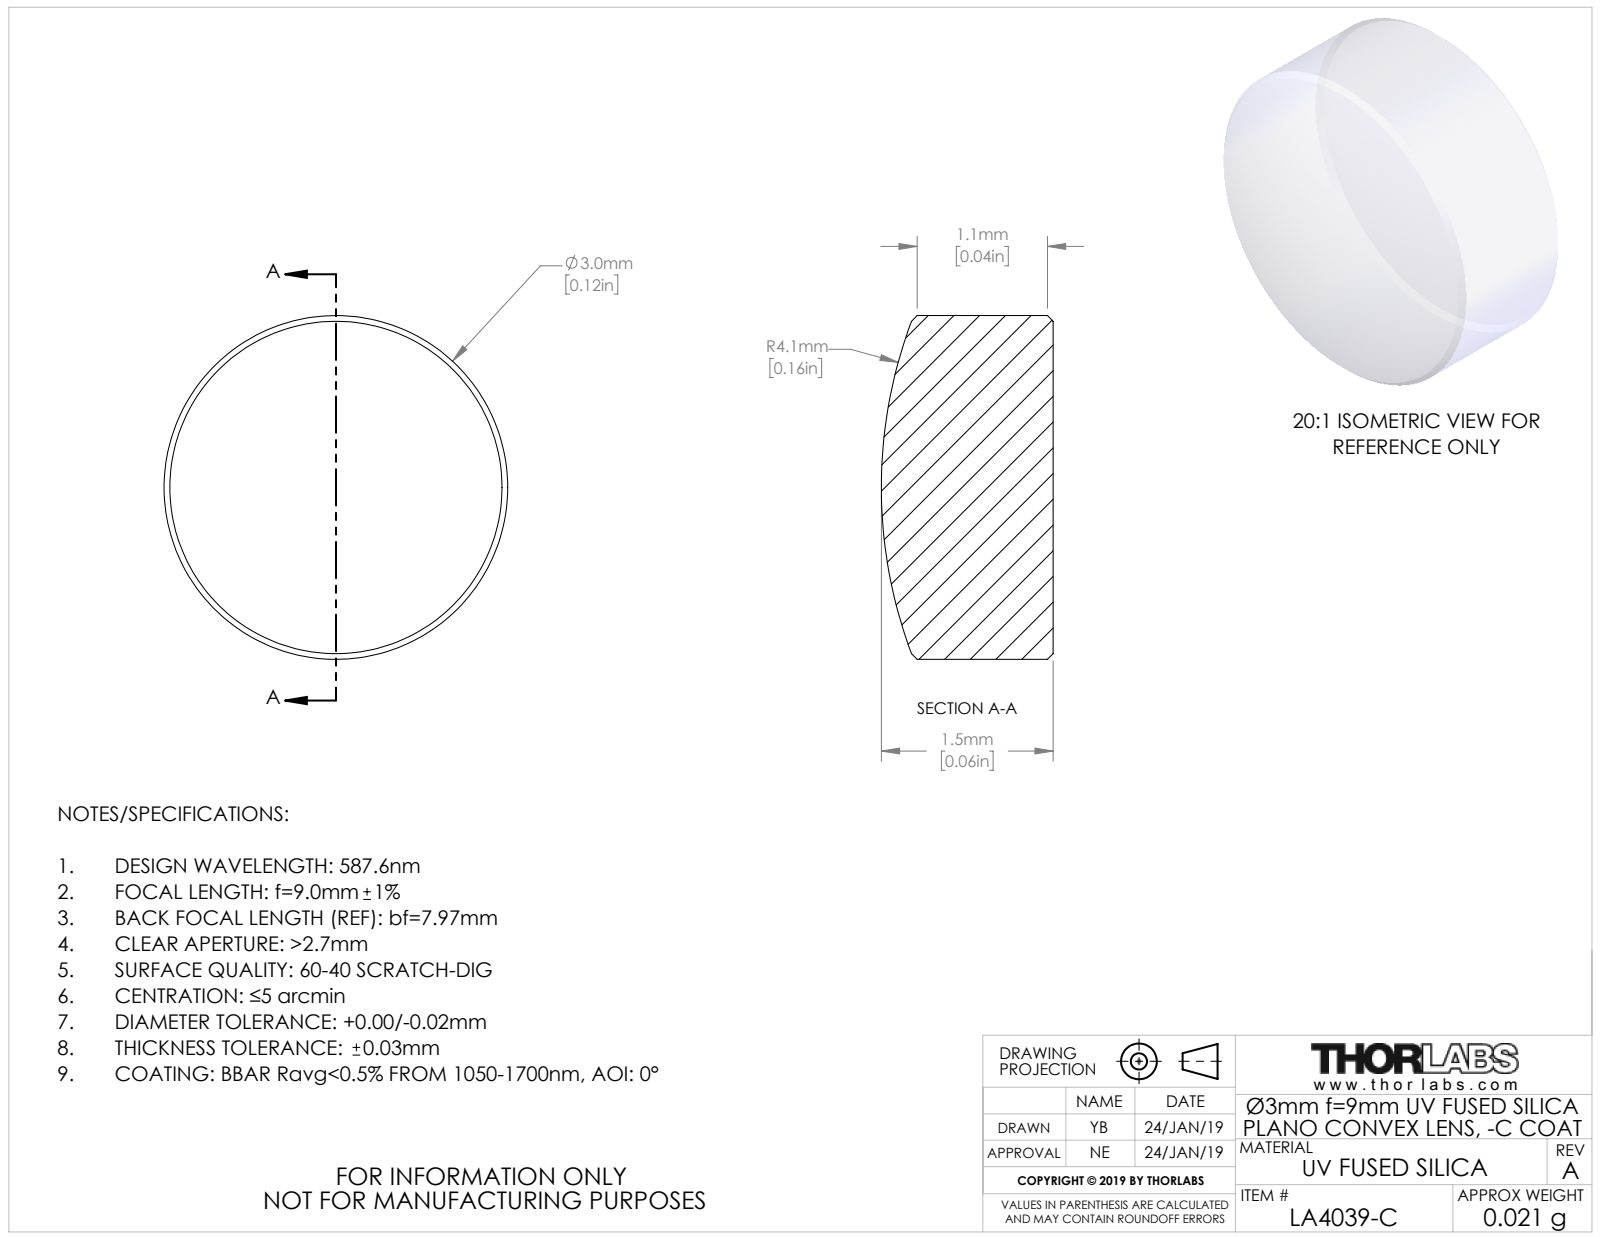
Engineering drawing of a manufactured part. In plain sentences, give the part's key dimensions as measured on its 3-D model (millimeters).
The part is named "TTN162823-E0W". Its 3-D file was written by "SolidWorks 2018 (CONFIG_CONTROL_DESIGN)". It is 1 solid with 9 faces: 1 planar, 2 cylindrical and 6 other. Overall it measures 3 by 3 by 1.5 millimeters. Its volume is 10 cubic millimeters and its surface area 25 square millimeters. Round bosses or shafts: 1 of diameter 3.
